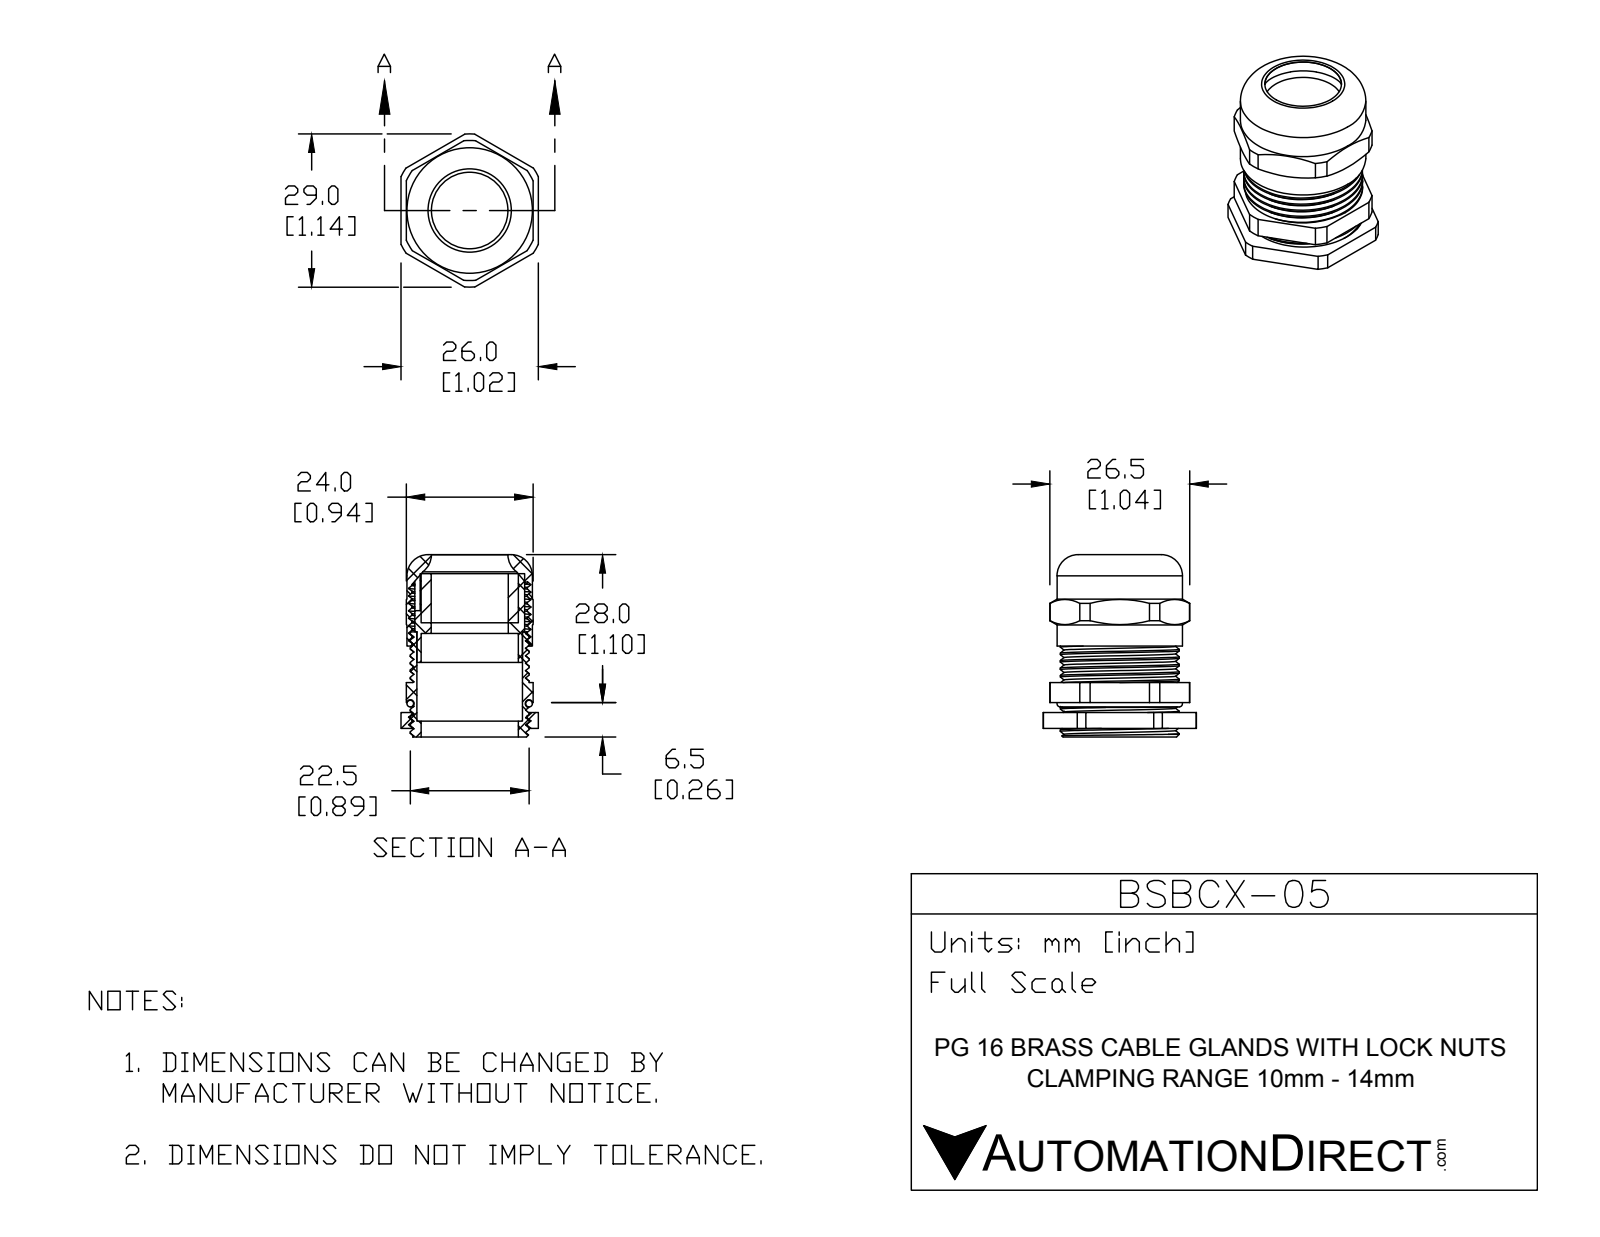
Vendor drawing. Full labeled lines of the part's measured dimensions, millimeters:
Part name (STEP PRODUCT): BSBCX-05
STEP written by: SolidWorks 2015 (CONFIG_CONTROL_DESIGN)
Units: millimetres
Bodies: 6 solids, 258 faces (135 planar, 91 cylindrical, 32 other)
Overall size (bounding box): 34.5 × 29 × 26
Volume: 6 265 mm³ · Surface area: 11 887 mm²
Round holes (diameter × count): ⌀14.5 ×1, ⌀14.6 ×1, ⌀18.4 ×1, ⌀20 ×1, ⌀21.83 ×1
Round bosses / shafts (diameter × count): ⌀23.75 ×1, ⌀22.5 ×1, ⌀20.8 ×1
Partial cylindrical surfaces — rounded edges, fillets, slot ends (radius × count): R13.25 ×1, R14.5 ×1
Main face-to-face distances: 24, 9.3, 3, 1, 25, 0.5, 11.3, 16.98, 19.98, 29.28
